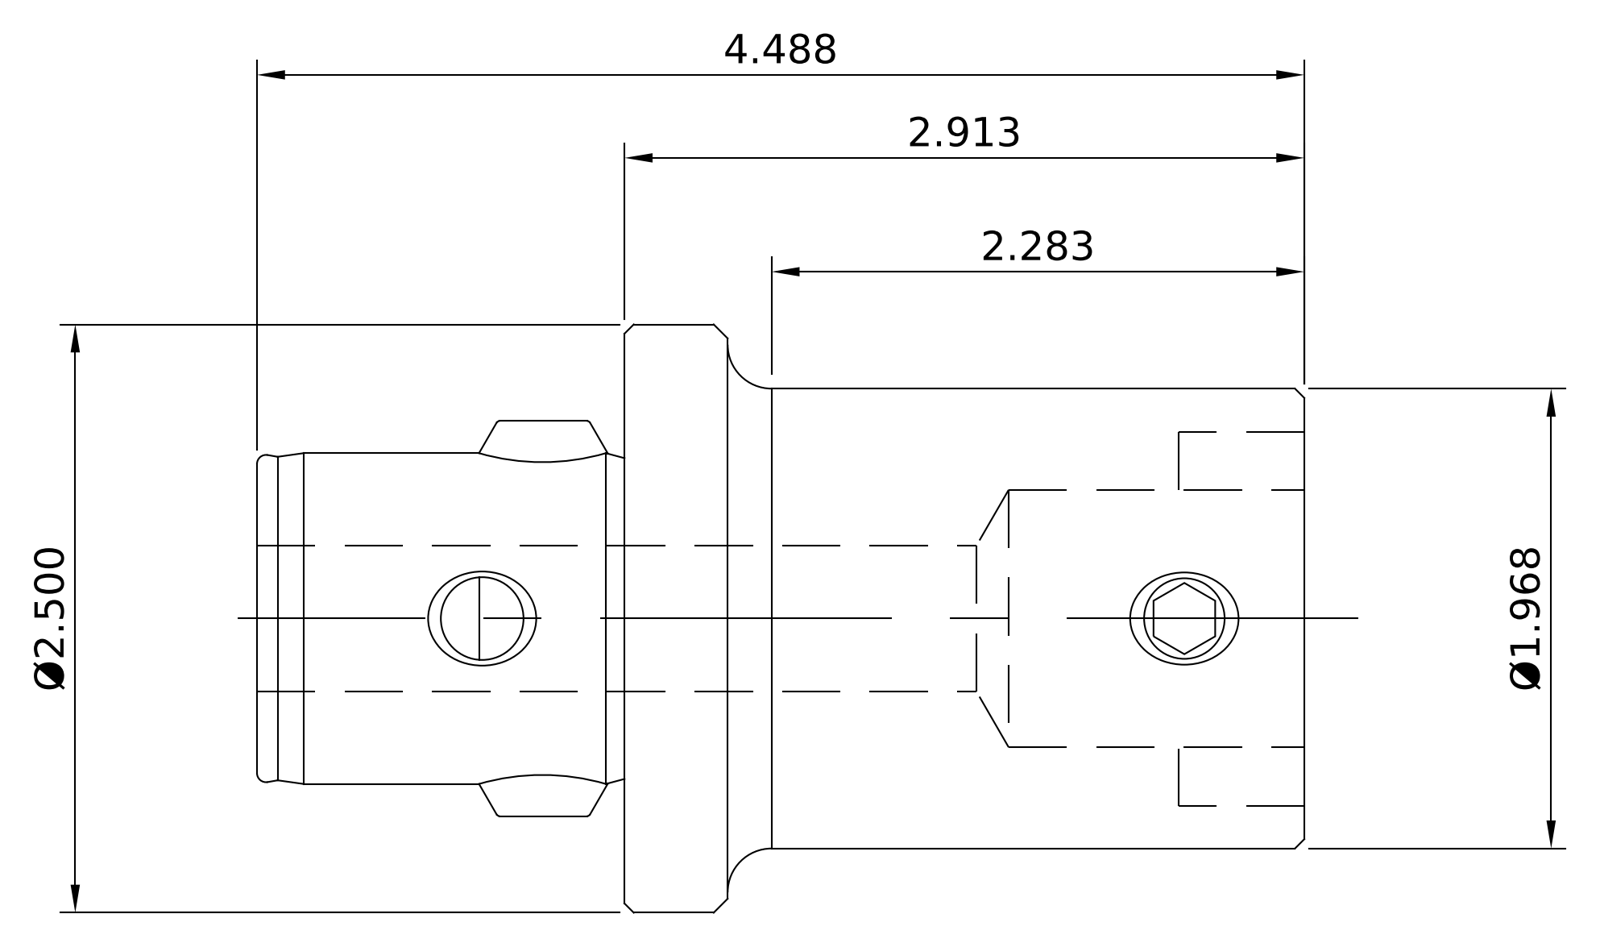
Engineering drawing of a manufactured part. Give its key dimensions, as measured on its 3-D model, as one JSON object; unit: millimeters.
{"part_name": "11.332.650; 10.691.50X_10.691.506; 691-50XRing_10.691.506Ring; 10.690.43X_10.690.435 (+1 more)", "step_written_by": "SolidWorks 2011 (AUTOMOTIVE_DESIGN)", "units": "millimeters", "bodies": {"solids": 4, "faces": 145, "planar": 42, "cylindrical": 49, "other": 54}, "overall_size": [114, 63.27, 63.27], "volume_mm3": 158491, "surface_area_mm2": 33164, "round_holes": [[8.5, 1], [9, 1], [10.3, 1], [14, 1], [16, 1], [18.5, 1], [22, 1], [28, 1], [28.5, 1]], "round_bosses_or_shafts": [[63.27, 1], [50, 1], [49.6, 1], [36, 1], [13.9, 1], [11.9, 1], [10, 1], [9.9, 1]], "partial_cylinders_radius": [[4.5, 2], [18, 1]], "face_to_face_distances": [74, 40, 114, 35, 79, 39, 21.4, 24.1, 27, 52], "hole_center_spacings": [76.45]}
